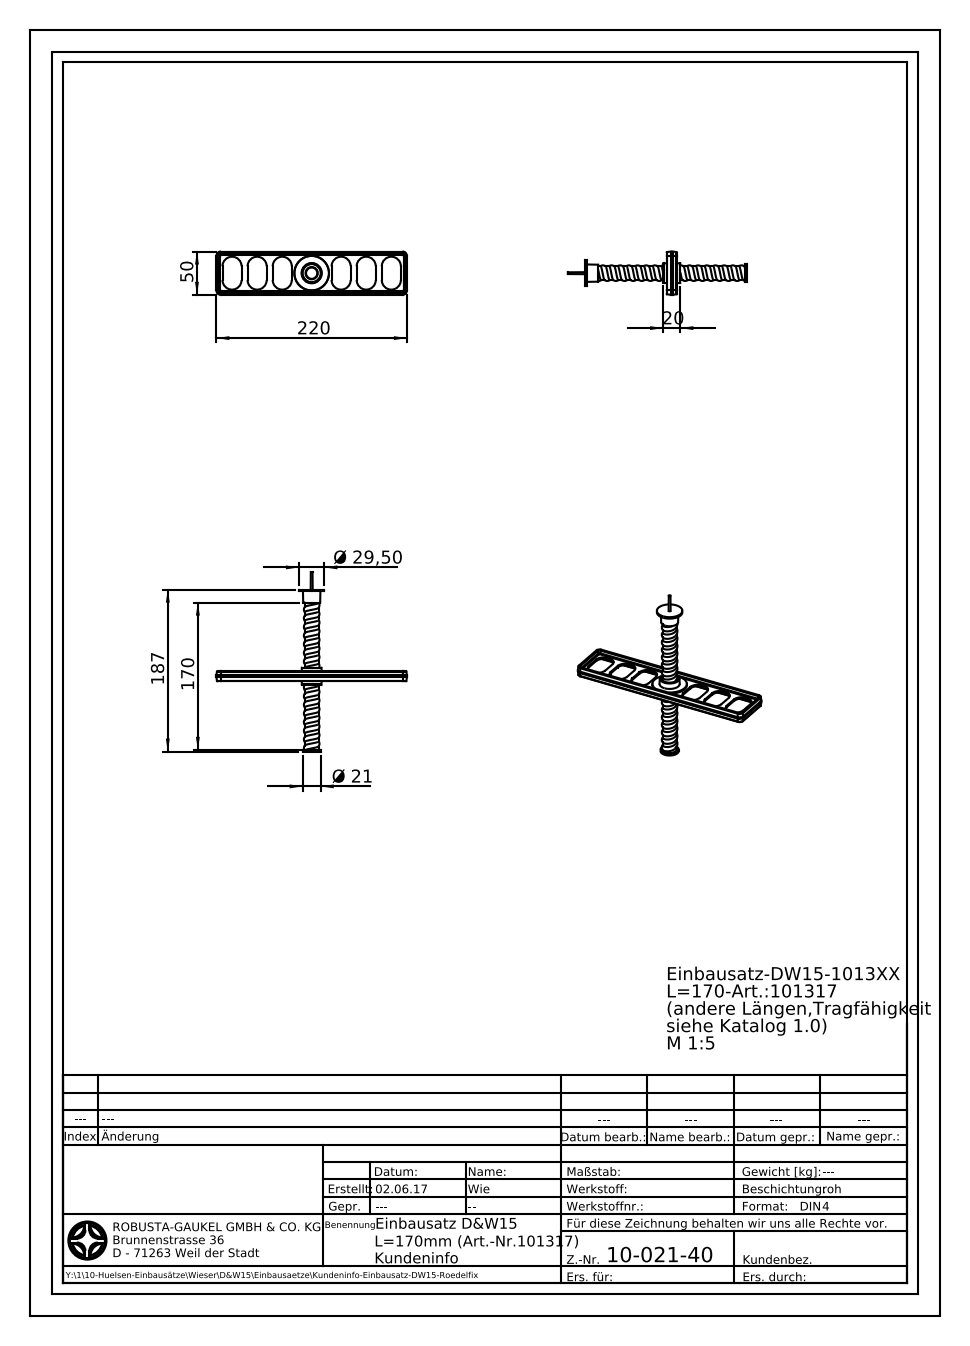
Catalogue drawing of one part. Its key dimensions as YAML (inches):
part_name: "Gewindehuelse-DW15_L=170-Art.:101517; Markierungsstopfen-15-101598; PVC-Kappe-15-101593; Kundeninfo-Einbausatz-DW15-L=170mm-Roedelfix (+1 more)"
step_written_by: "SolidWorks 2018 (AUTOMOTIVE_DESIGN)"
units: inches
bodies: {solids: 4, faces: 236, planar: 51, cylindrical: 116, other: 69}
overall_size: [8.661, 8.15, 1.969]
volume: 2.457
surface_area: 76.4
round_holes:
  - {diameter: 0.61, count: 1}
  - {diameter: 0.772, count: 1}
round_bosses_or_shafts:
  - {diameter: 1.161, count: 1}
  - {diameter: 0.827, count: 1}
  - {diameter: 0.63, count: 1}
partial_cylinders:
  - {radius: 0.433, count: 12}
  - {radius: 0.036, count: 8}
  - {radius: 0.039, count: 8}
  - {radius: 0.197, count: 4}
face_to_face_distances: [0.079, 0.128, 1.832, 1.96, 0.059, 0.138, 1.704, 2.717, 0.197, 2.854]
